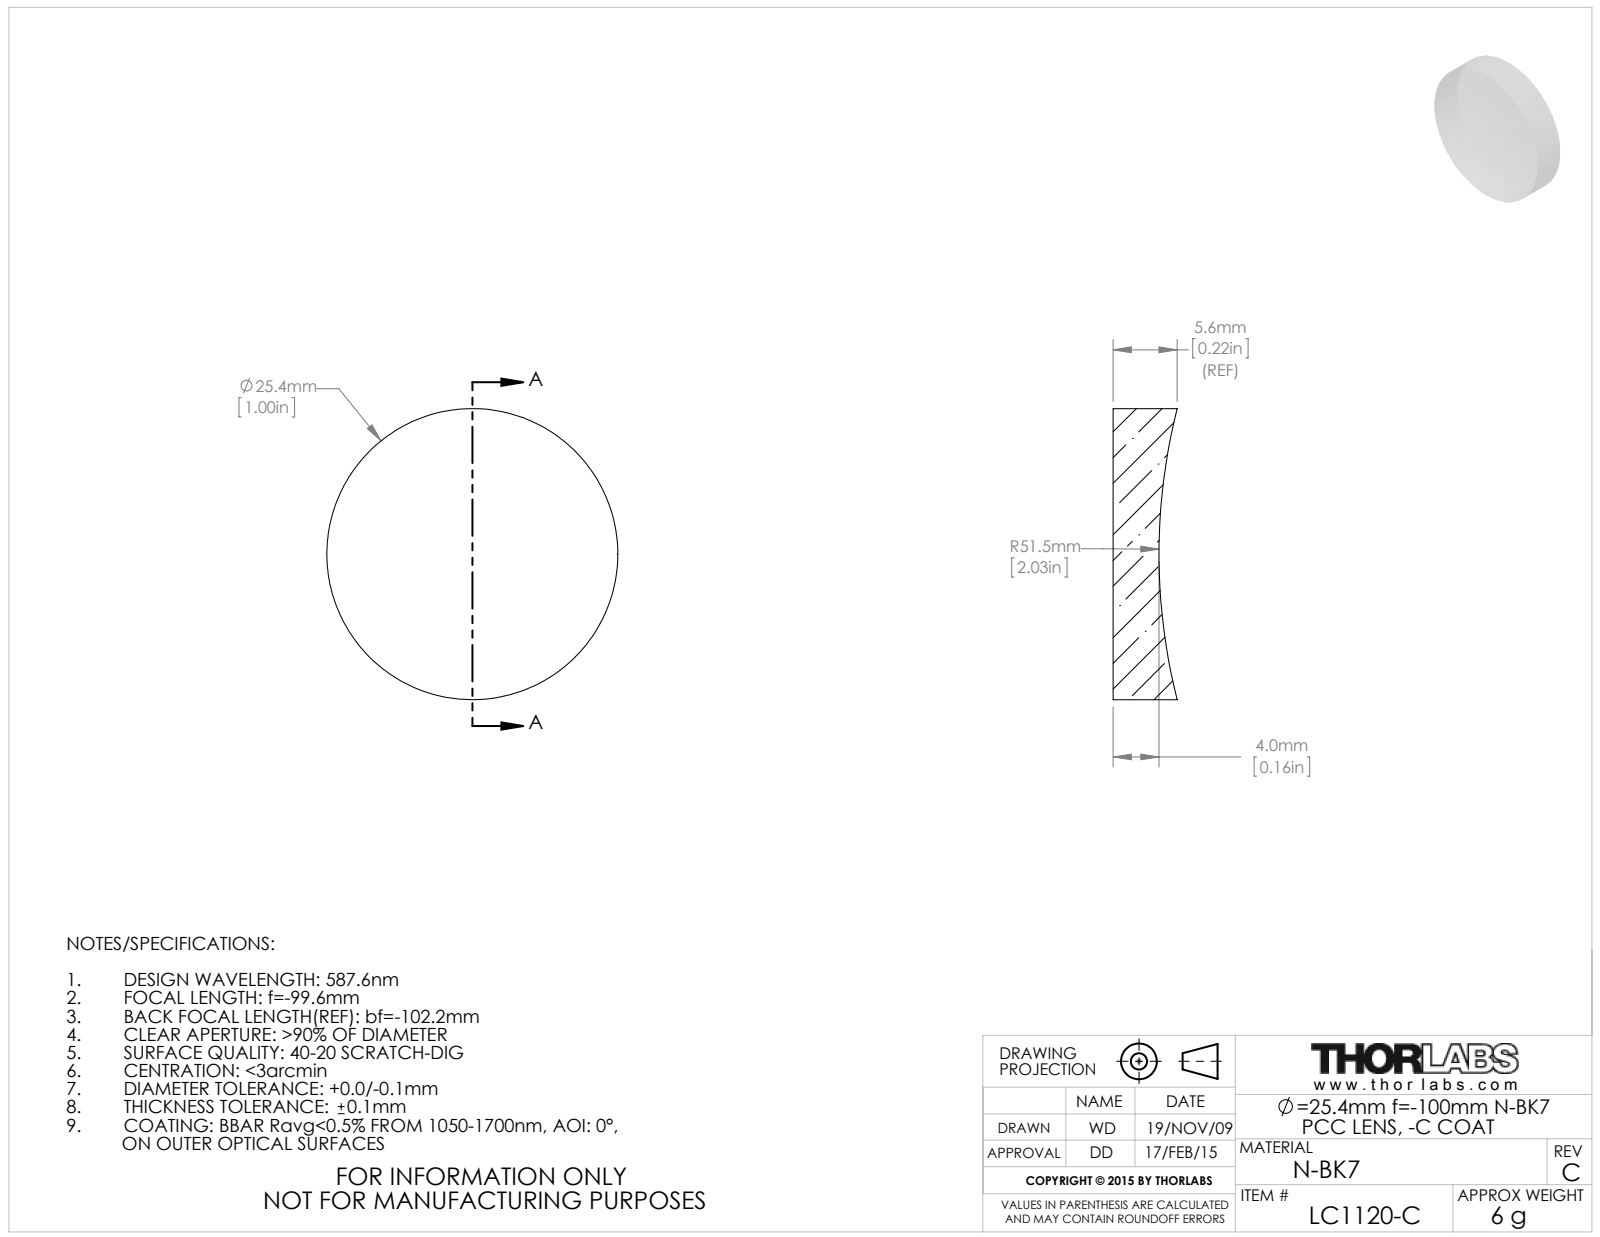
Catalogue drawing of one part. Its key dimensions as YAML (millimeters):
part_name: "4806-E0W"
step_written_by: "SolidWorks 2009 (AUTOMOTIVE_DESIGN)"
units: millimeters
bodies: {solids: 1, faces: 5, planar: 1, cylindrical: 2, other: 2}
overall_size: [25.4, 25.4, 5.59]
volume: 2428
surface_area: 1468
round_bosses_or_shafts:
  - {diameter: 25.4, count: 1}
